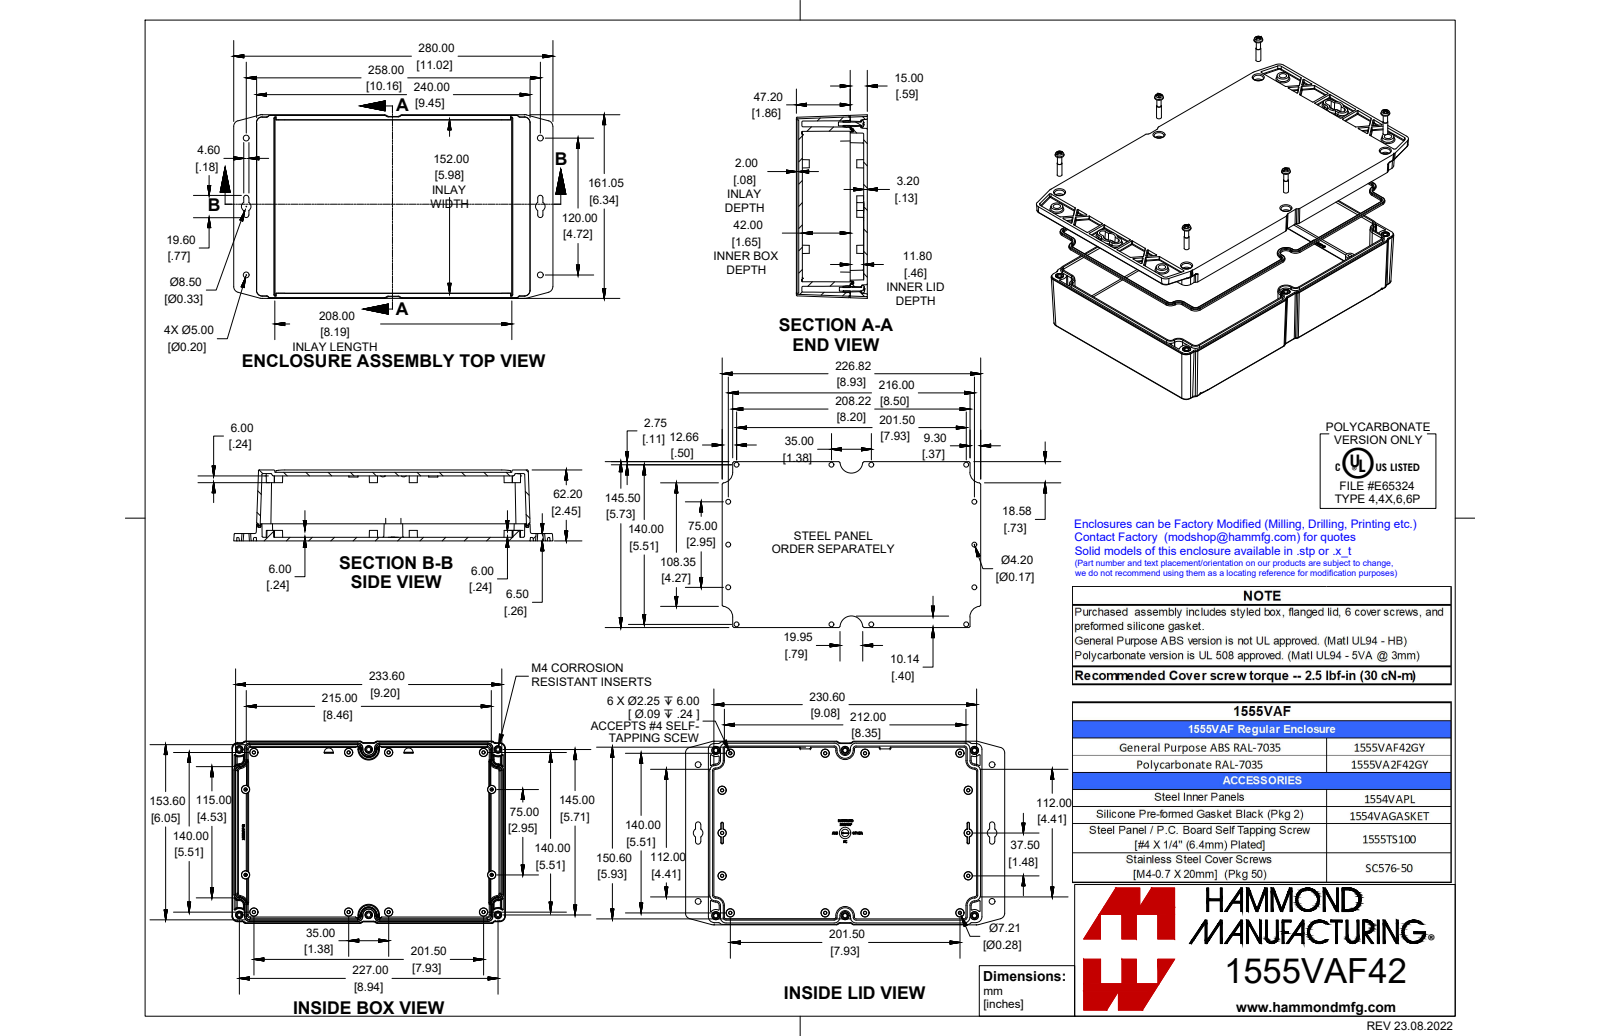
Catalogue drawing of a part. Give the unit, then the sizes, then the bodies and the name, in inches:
Units: inches
Overall size (bounding box): 11.024 × 6.34 × 2.449
Round holes (diameter × count): ⌀0.128 ×6, ⌀0.158 ×6
Round bosses / shafts (diameter × count): ⌀0.276 ×6, ⌀0.153 ×6, ⌀0.138 ×6
Partial cylindrical surfaces — rounded edges, fillets, slot ends (radius × count): R0.02 ×130, R0.031 ×43, R0.012 ×22, R0.079 ×16, R0.039 ×14, R0.1 ×12, R0.195 ×12, R0.024 ×8
Main face-to-face distances: 0.126, 2.244, 2.37, 2.118, 0.079, 0.118, 0.256, 2.323, 0.472, 0.047
Hole centre spacings: 4.469, 7.25, 5.709, 8.937, 10.605
Volume: 27.71 in³ · Surface area: 452 in²
Bodies: 9 solids, 1874 faces (610 planar, 436 cylindrical, 828 other)
Part name (STEP PRODUCT): 1555VAF42GY
STEP written by: SolidWorks 2021 (AUTOMOTIVE_DESIGN)
